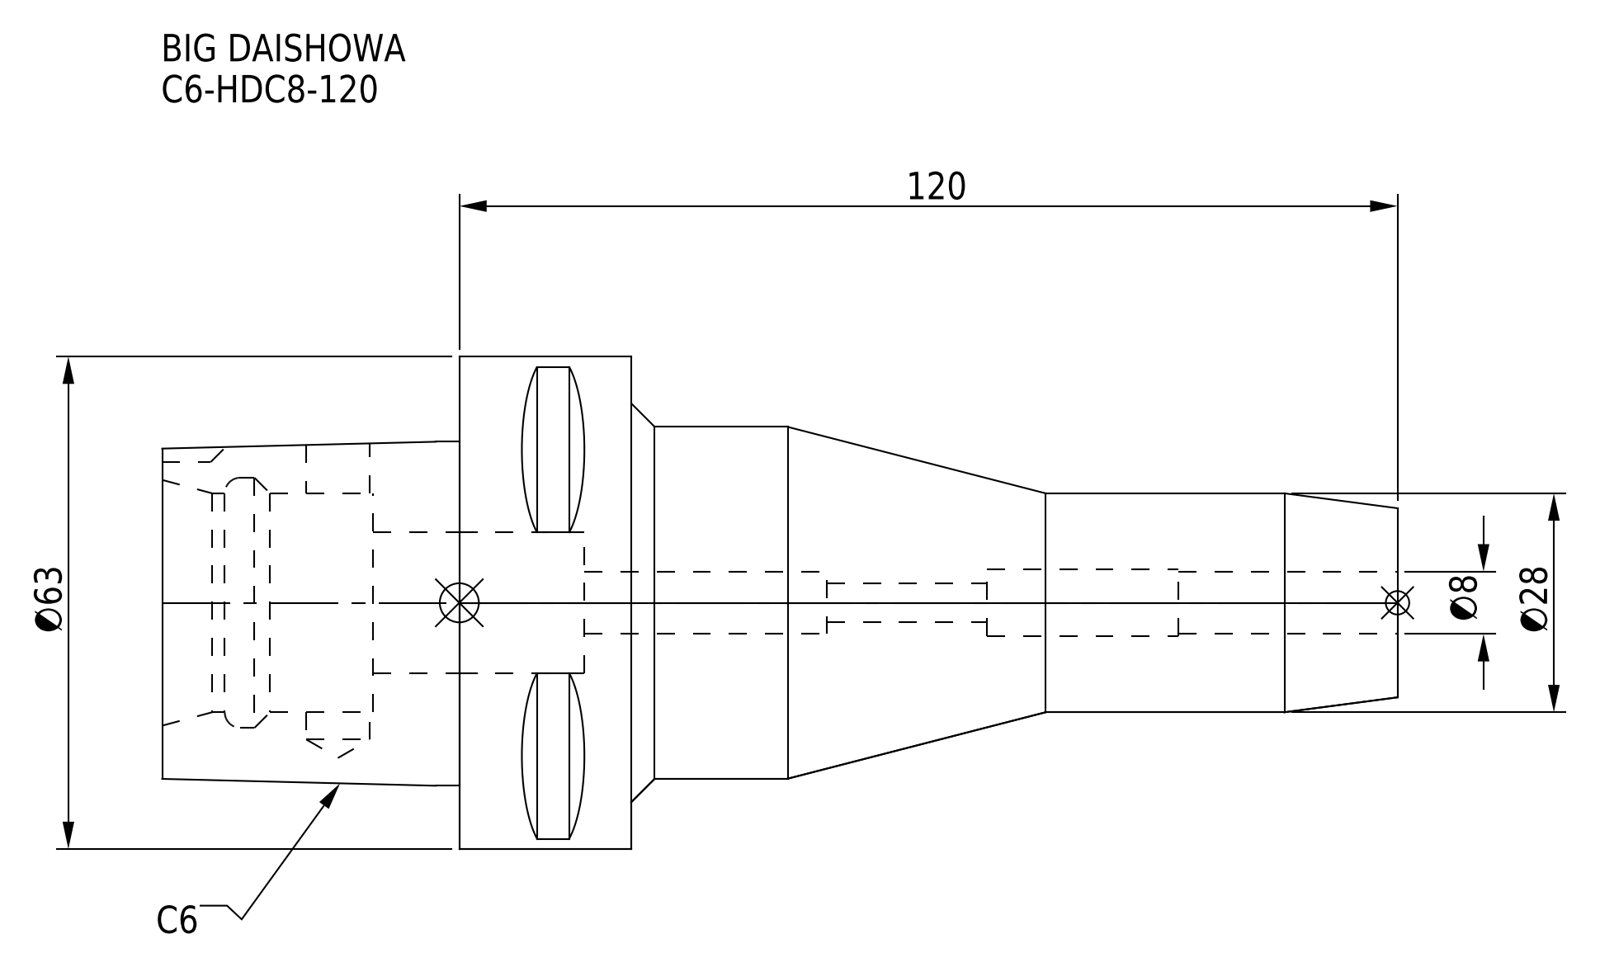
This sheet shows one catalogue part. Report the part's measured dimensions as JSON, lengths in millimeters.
{"part_name": "C6-HDC8-120", "step_written_by": "CREO PARAMETRIC BY PTC INC, 2016380 (AUTOMOTIVE_DESIGN)", "units": "millimeters", "bodies": {"solids": 1, "faces": 74, "planar": 31, "cylindrical": 27, "other": 16}, "overall_size": [158, 63, 63], "volume_mm3": 186005, "surface_area_mm2": 31832, "round_holes": [[5, 1], [8, 1], [8.1, 1], [8.5, 1], [18, 1], [28, 1], [32, 1]], "round_bosses_or_shafts": [[63, 1], [45, 1]], "partial_cylinders_radius": [[5, 1]], "face_to_face_distances": [22, 27, 60, 38, 98, 120, 158, 131, 33, 11]}
